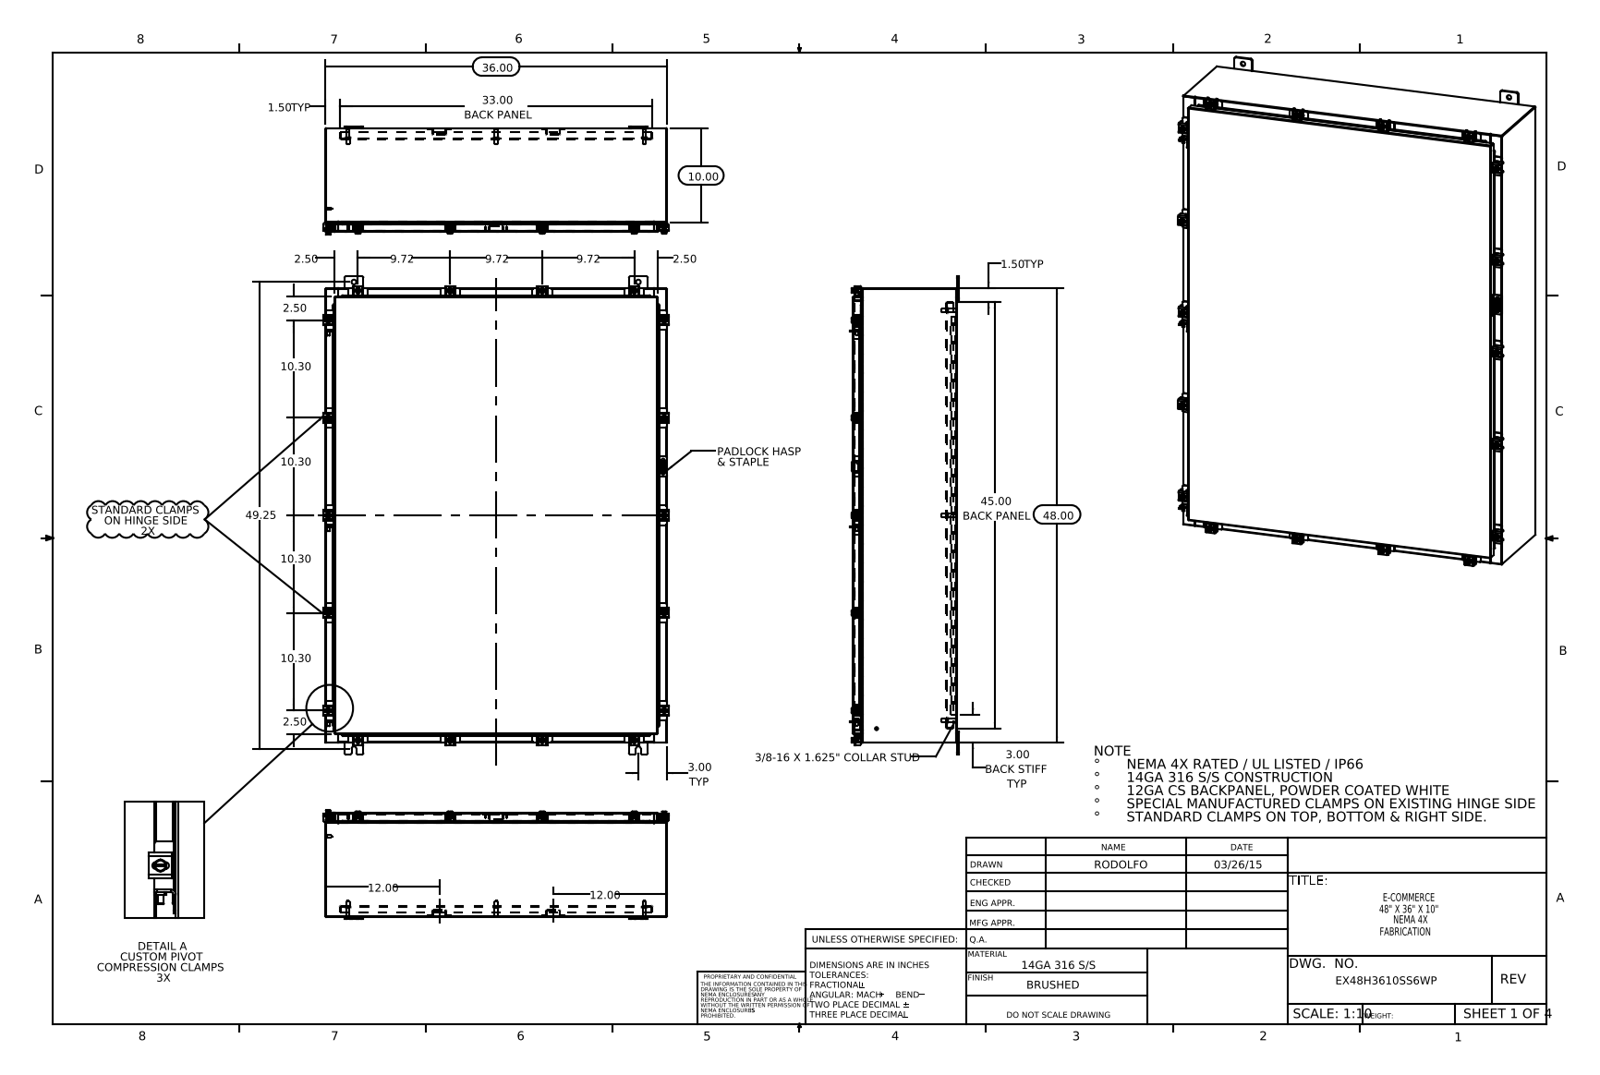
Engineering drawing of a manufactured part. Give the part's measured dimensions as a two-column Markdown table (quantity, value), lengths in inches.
| quantity | value |
| --- | --- |
| part name | 30X10 Clamp Bracket2; EX48H3610SS6WP Padlock Hasp; 22104005_DEFAULT_RTP30; EX48H3610SS6WP Special Clamp (+8 more) |
| STEP written by | SolidWorks 2014 (CONFIG_CONTROL_DESIGN) |
| units | inches |
| bodies | 128 solids, 3145 faces (1631 planar, 1216 cylindrical, 298 other) |
| overall size | 50.5 × 36.421 × 11.453 |
| volume | 623.8 in³ |
| surface area | 15 472 in² |
| round holes (diameter × count) | 0.213 × 18, 0.26 × 18, 0.5 × 12, 0.25 × 7, 0.125 × 1 |
| round bosses / shafts (diameter × count) | 0.5 × 18, 0.25 × 18, 0.399 × 15, 0.625 × 8, 0.375 × 8, 0.33 × 8, 0.157 × 6, 0.14 × 6 |
| partial cylindrical surfaces (radius × count) | 0.06 × 76, 0.013 × 38, 0.141 × 36, 0.088 × 34, 0.12 × 33, 0.05 × 27, 0.09 × 27, 0.145 × 26 |
| main face-to-face distances | 0.075, 10.9, 10.826, 10.975, 0.104, 1, 1.075, 9.826, 9.9, 1.179 |
| hole center spacings | 1.969, 2.347, 4.44, 13.972, 14.728, 16.126, 16.624, 17.756 |
